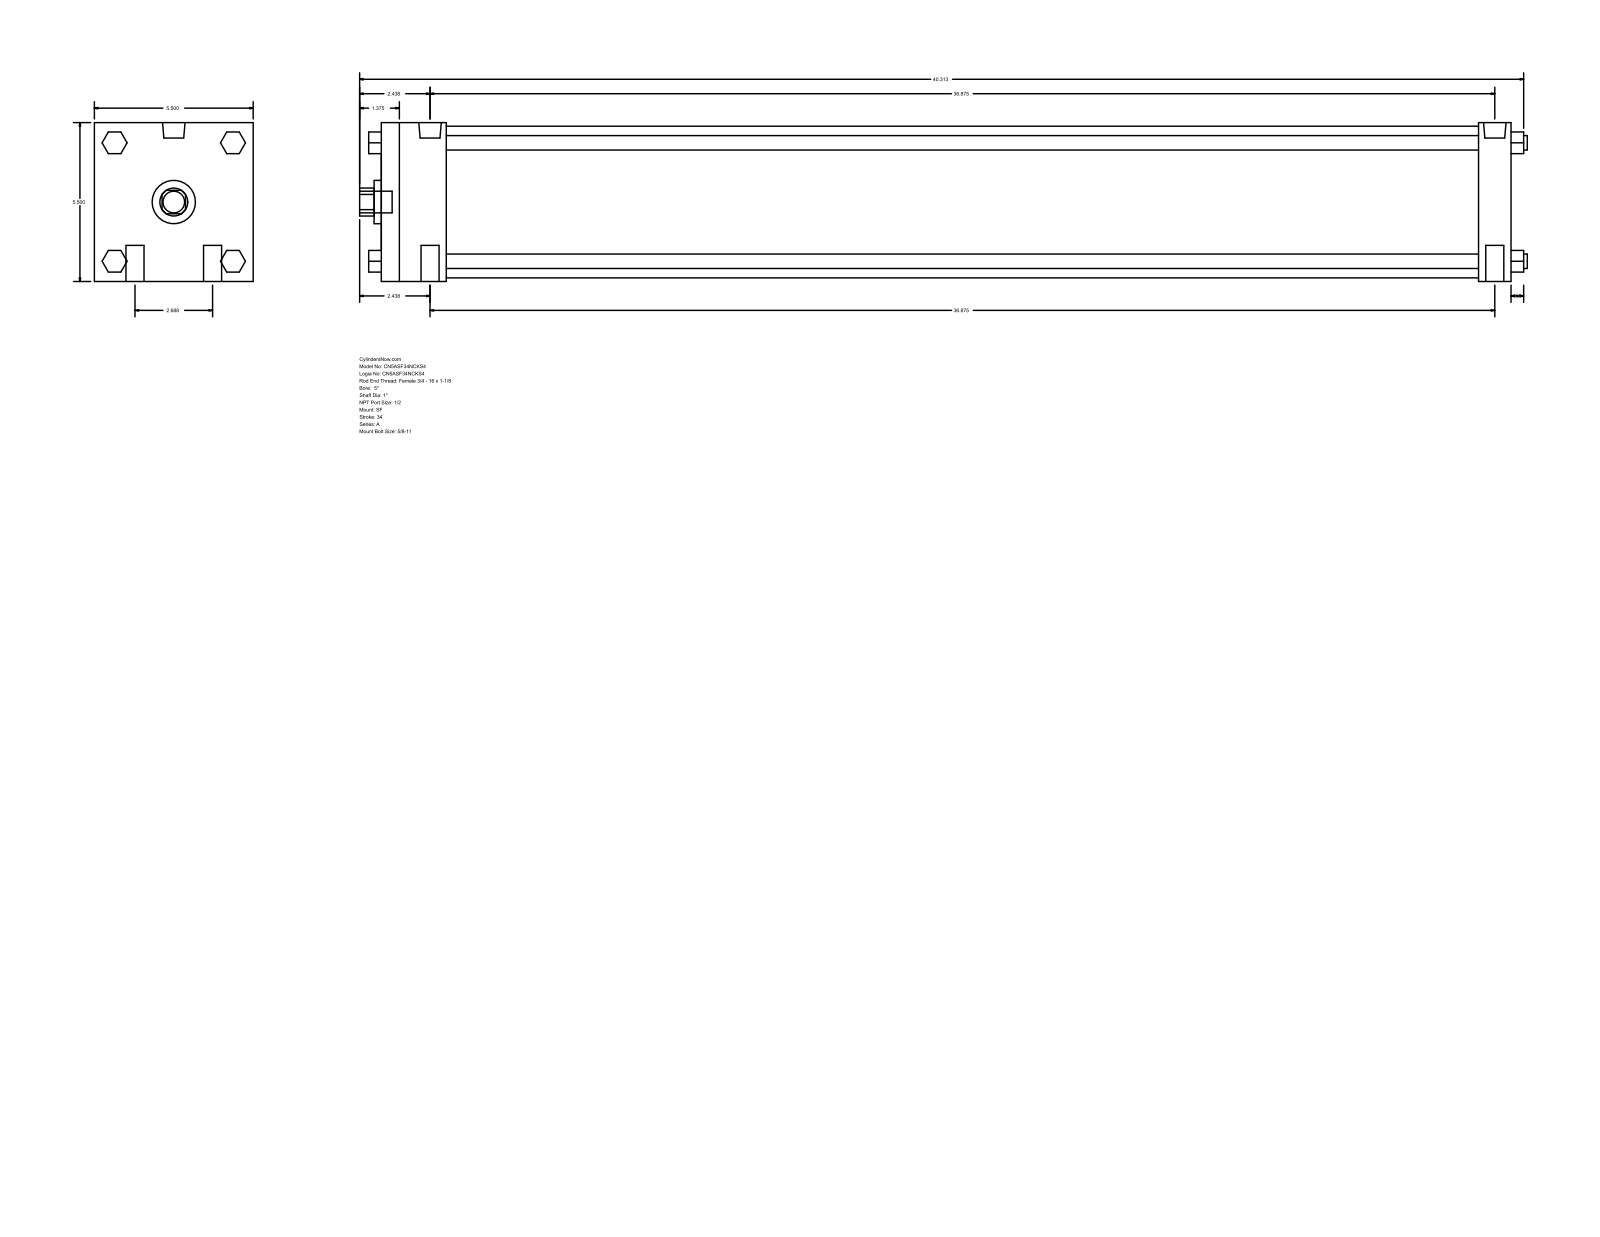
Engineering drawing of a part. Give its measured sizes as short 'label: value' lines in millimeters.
name: A_SF__0500_1
written by: GSSL Pune (CONFIG_CONTROL_DESIGN)
unit: mm
bodies: 0 solids, 124 faces (94 planar, 30 cylindrical, 0 other)
size: 1027.11 × 139.7 × 139.7
holes: 1× ⌀25.4, 1× ⌀38.1, 1× ⌀133.35
bosses: 4× ⌀15.88, 4× ⌀12.7, 2× ⌀19.77, 2× ⌀8.73, 1× ⌀19.05
rounds: 1× R12.29
face distances: 139.7, 993.78, 57.15, 965.2, 908.05, 936.63, 28.58, 19.05, 52.07, 90.18
